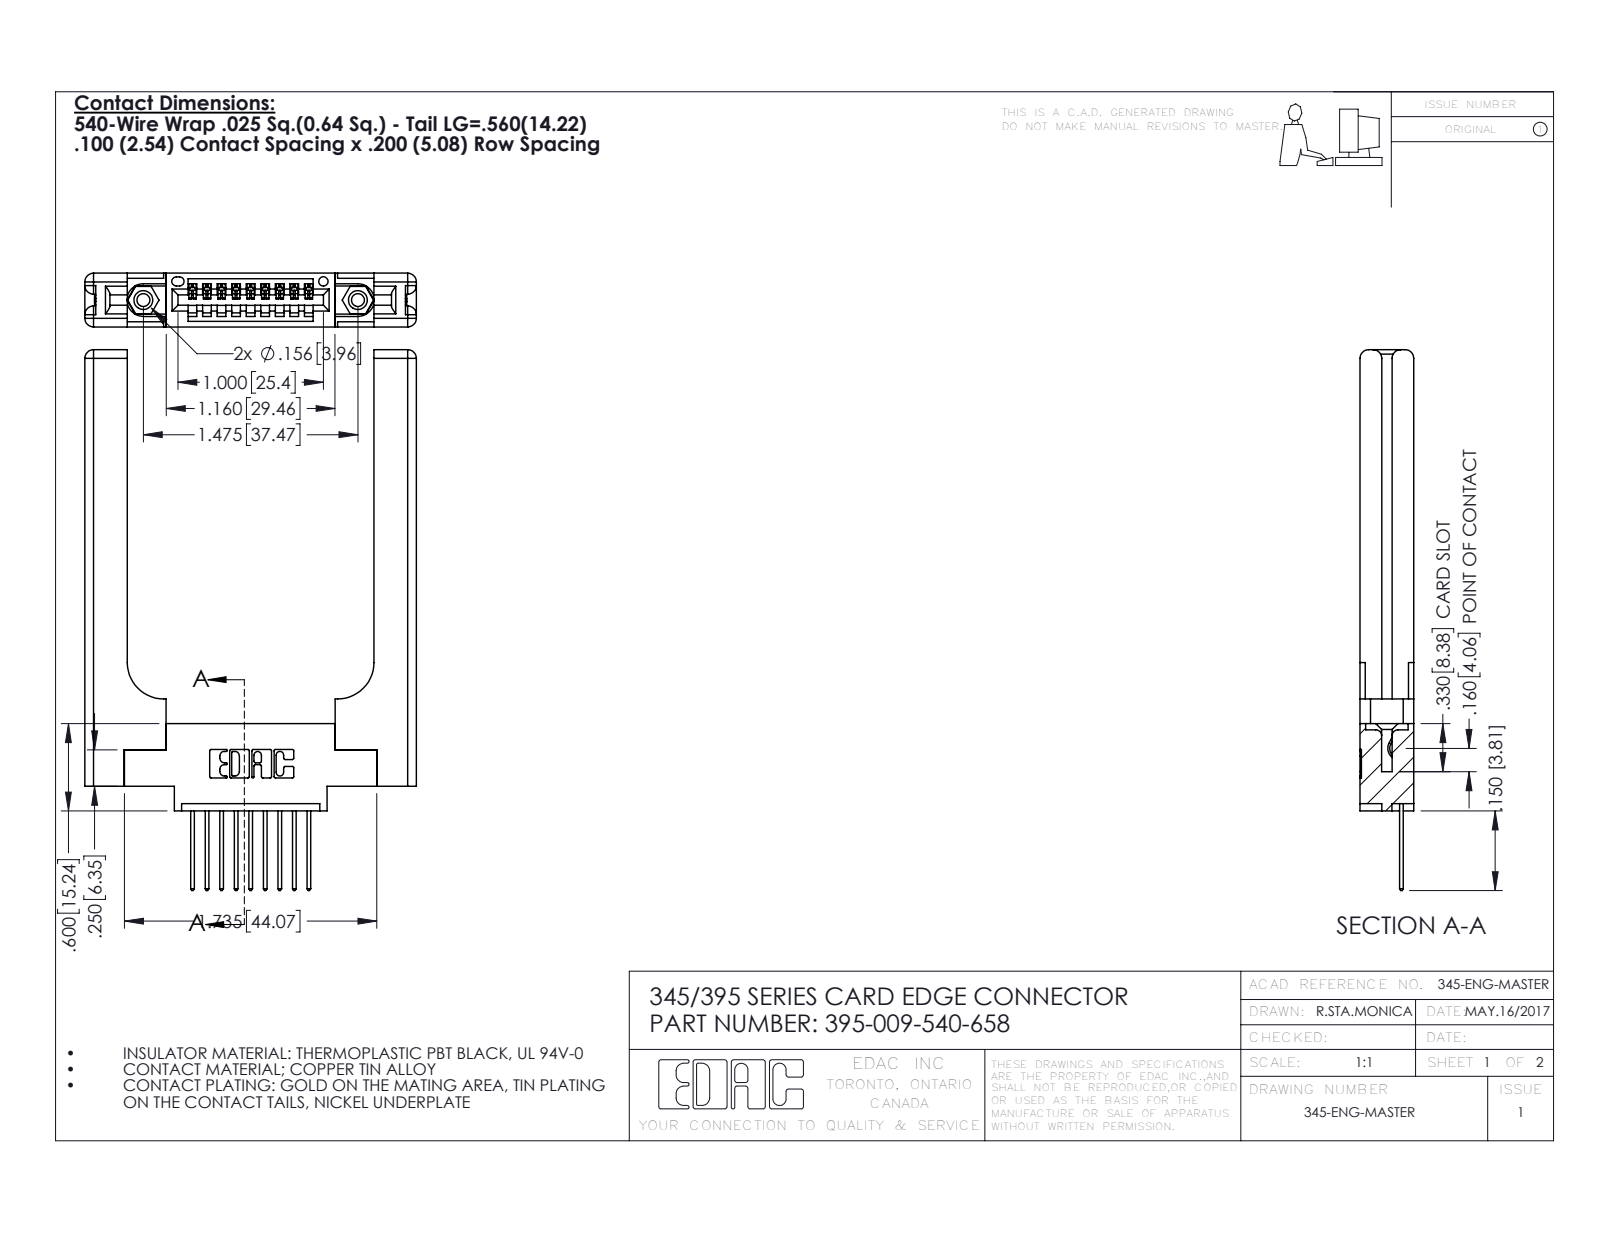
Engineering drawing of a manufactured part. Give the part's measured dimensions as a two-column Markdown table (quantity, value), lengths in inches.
| quantity | value |
| --- | --- |
| part name | 345 Part_0.170 Offset - 0.156 Dia-TH; 345-292-001_345-293-140; 395-009-540-658; 345-220-058_345-220-058 (+1 more) |
| STEP written by | SolidWorks 2016 (CONFIG_CONTROL_DESIGN) |
| units | inches |
| bodies | 14 solids, 908 faces (592 planar, 256 cylindrical, 60 other) |
| overall size | 3.717 × 2.279 × 0.37 |
| volume | 0.832 in³ |
| surface area | 18.42 in² |
| round holes (diameter × count) | 0.089 × 2, 0.125 × 2, 0.156 × 2, 0.064 × 1 |
| round bosses / shafts (diameter × count) | 0.155 × 2 |
| partial cylindrical surfaces (radius × count) | 0.01 × 22, 0.006 × 18, 0.01 × 18, 0.06 × 16, 0.007 × 6, 0.031 × 6, 0.026 × 3, 0.03 × 2 |
| main face-to-face distances | 0.37, 0.15, 0.072, 0.22, 0.077, 0.148, 0.298, 1.696, 0.071, 0.12 |
| hole center spacings | 0.27, 1.244, 1.475 |
